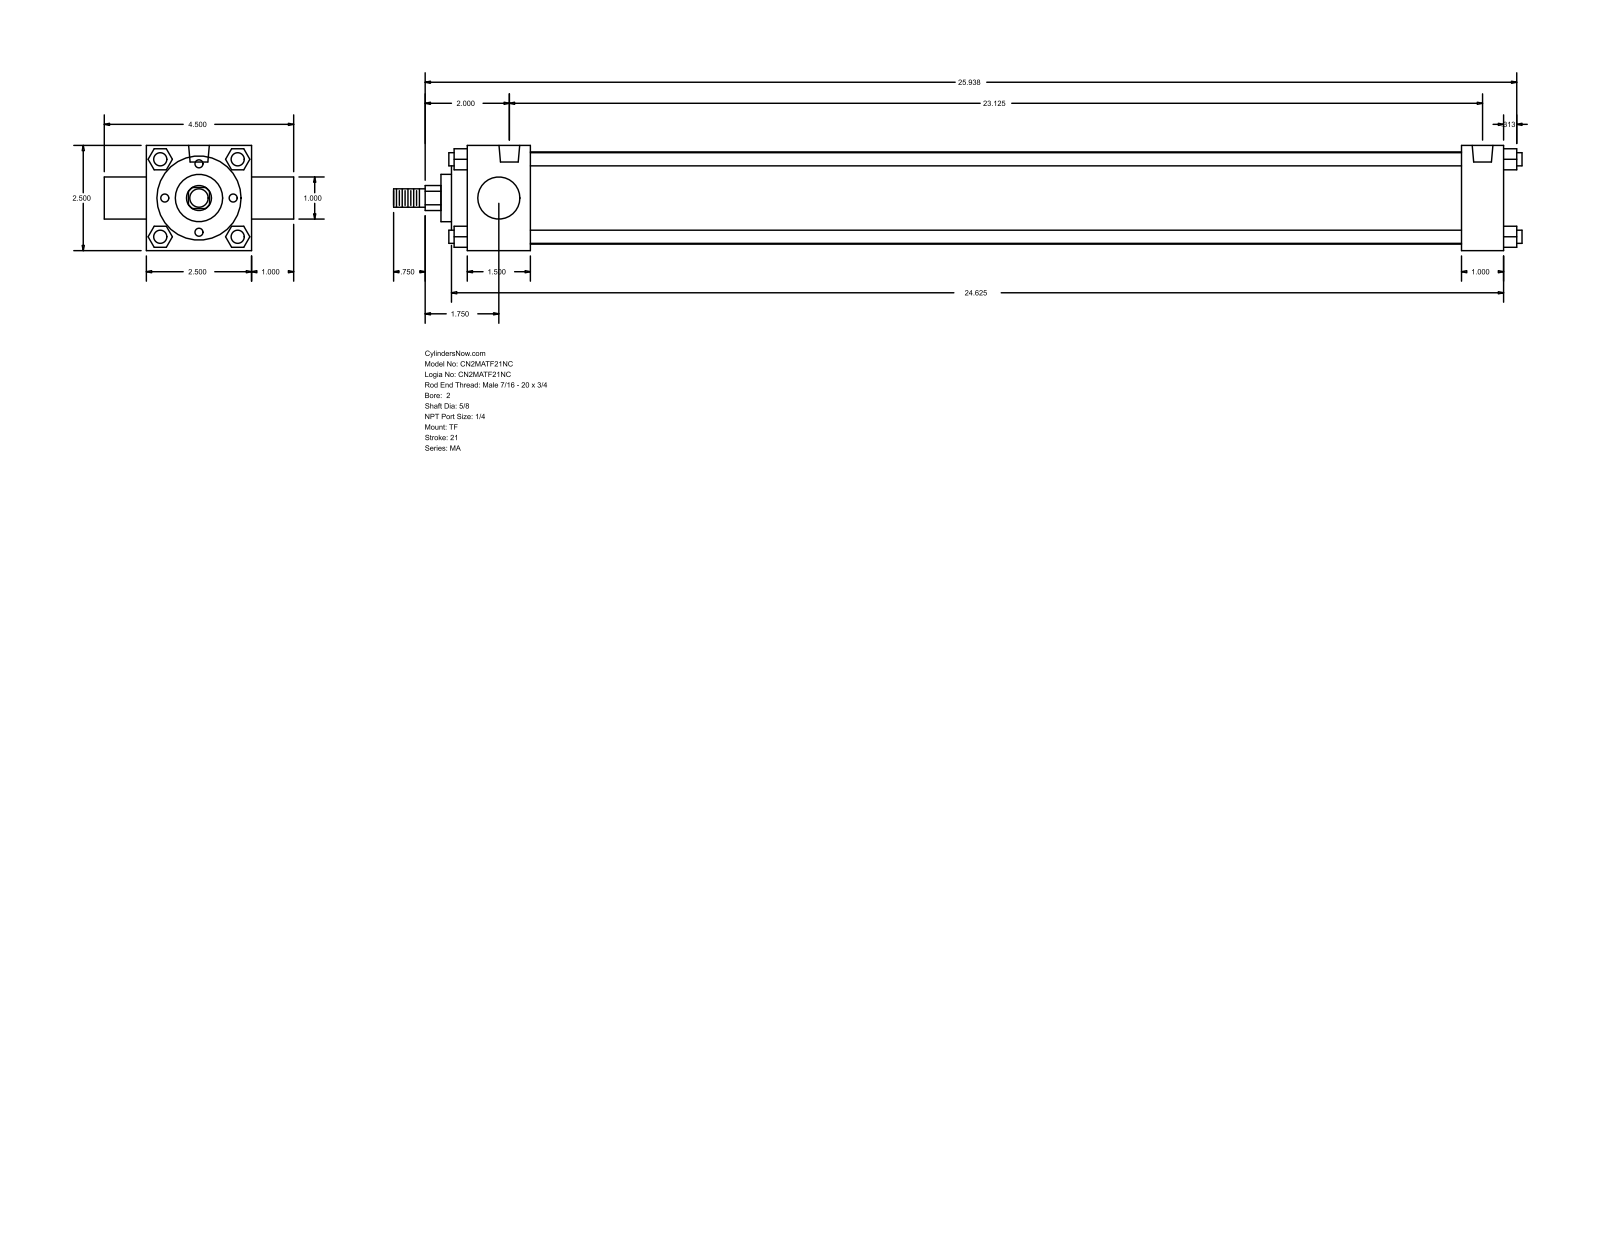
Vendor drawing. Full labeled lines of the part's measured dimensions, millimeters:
Part name (STEP PRODUCT): MA_TF__0200_0.625
STEP written by: GSSL Pune (CONFIG_CONTROL_DESIGN)
Units: millimetres
Bodies: 0 solids, 122 faces (93 planar, 29 cylindrical, 0 other)
Overall size (bounding box): 681.04 × 114.3 × 63.5
Round holes (diameter × count): ⌀7.94 ×3, ⌀12.49 ×2
Round bosses / shafts (diameter × count): ⌀7.94 ×4, ⌀55.63 ×1, ⌀50.8 ×1, ⌀28.57 ×1, ⌀25.4 ×1, ⌀15.88 ×1, ⌀11.11 ×1
Partial cylindrical surfaces — rounded edges, fillets, slot ends (radius × count): R7.54 ×1
Main face-to-face distances: 63.5, 25.4, 38.1, 625.48, 12.7, 600.08, 561.98, 587.38, 9.52, 47.62
Hole centre spacings: 587.37
